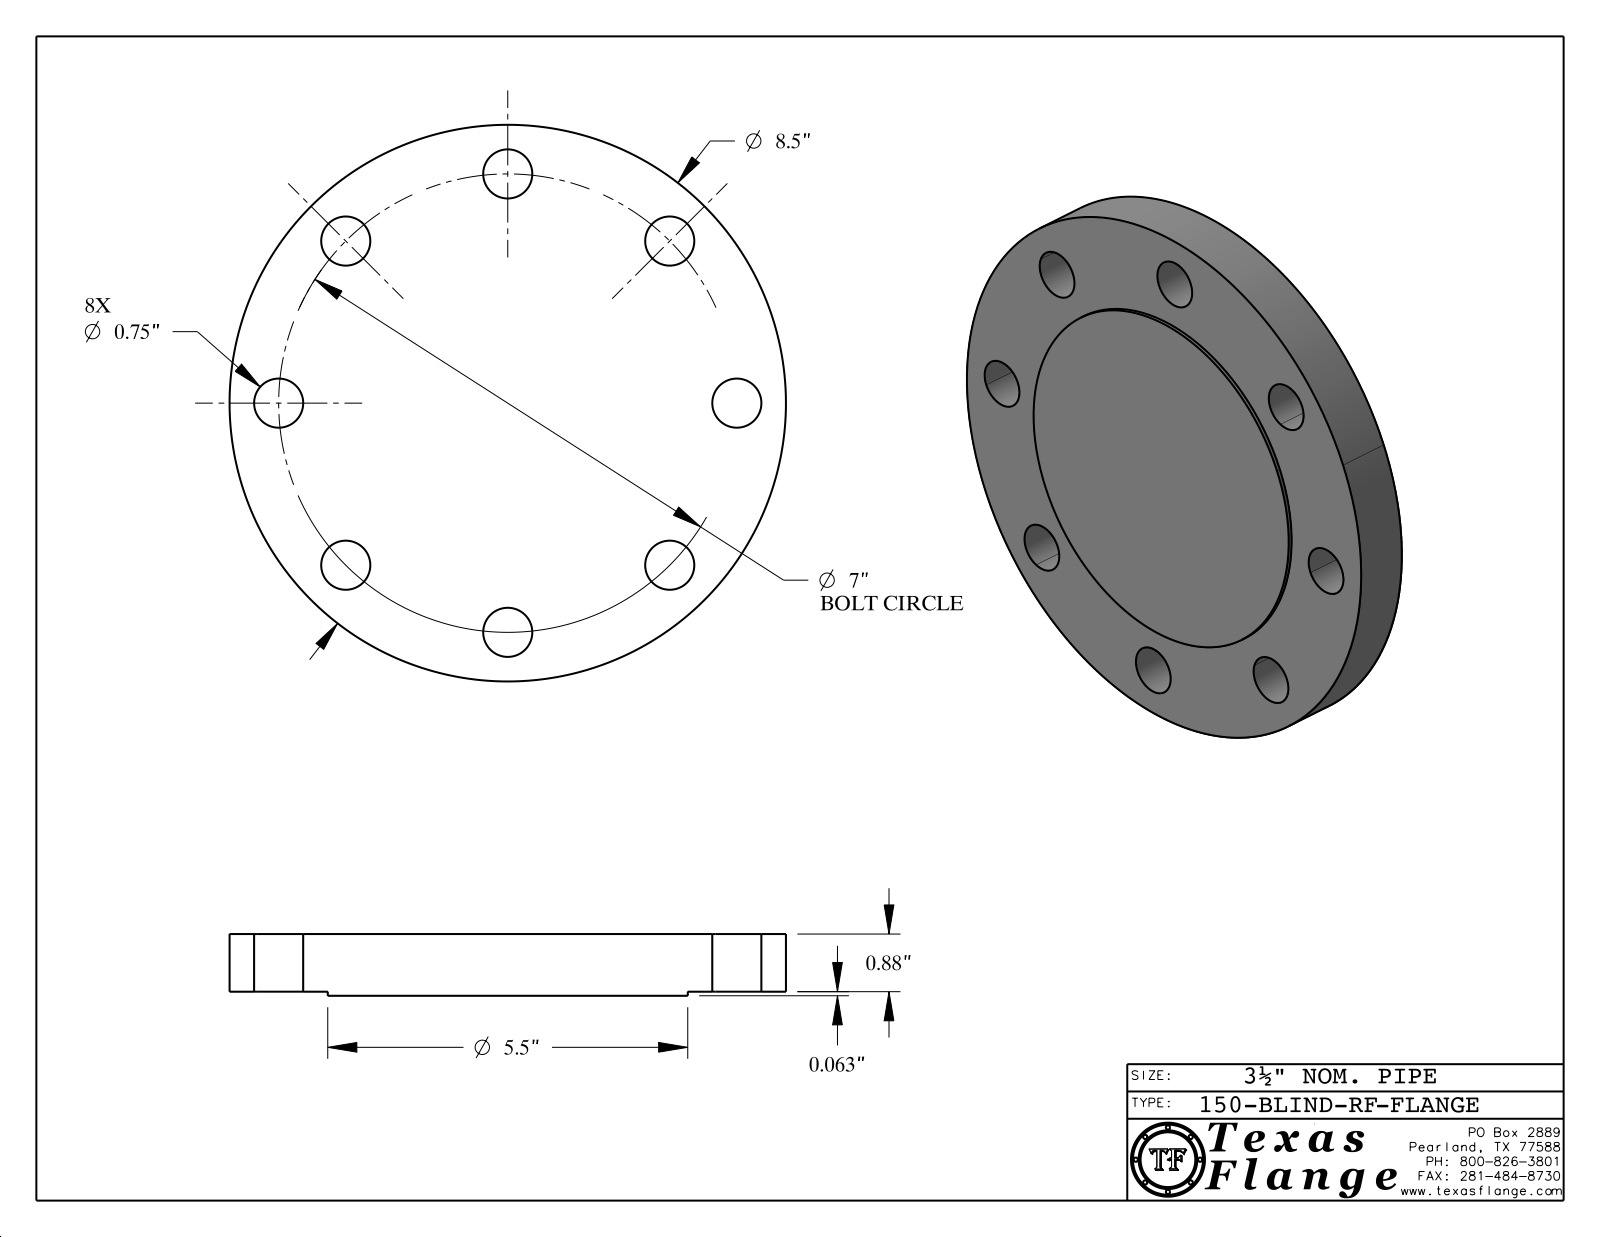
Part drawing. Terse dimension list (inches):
name: 150-BLIND-RF
written by: CATIA V5 STEP AP214 (AUTOMOTIVE_DESIGN)
unit: in
bodies: 1 solid, 408 faces (368 planar, 40 cylindrical, 0 other)
size: 8.5 × 8.5 × 0.943
volume: 48.31 in³; area: 147.7 in²
holes: 8× ⌀0.75, 1× ⌀0.495
bosses: 8× ⌀0.03, 1× ⌀8.5, 1× ⌀5.5, 1× ⌀0.39
face distances: 0.88, 0.063, 0.943, 0.928, 0.865, 0.015, 0.148, 0.145, 0.027, 0.122
hole spacings: 2.679, 4.95, 6.467, 1.366, 3.889, 5.82, 6.865, 7
